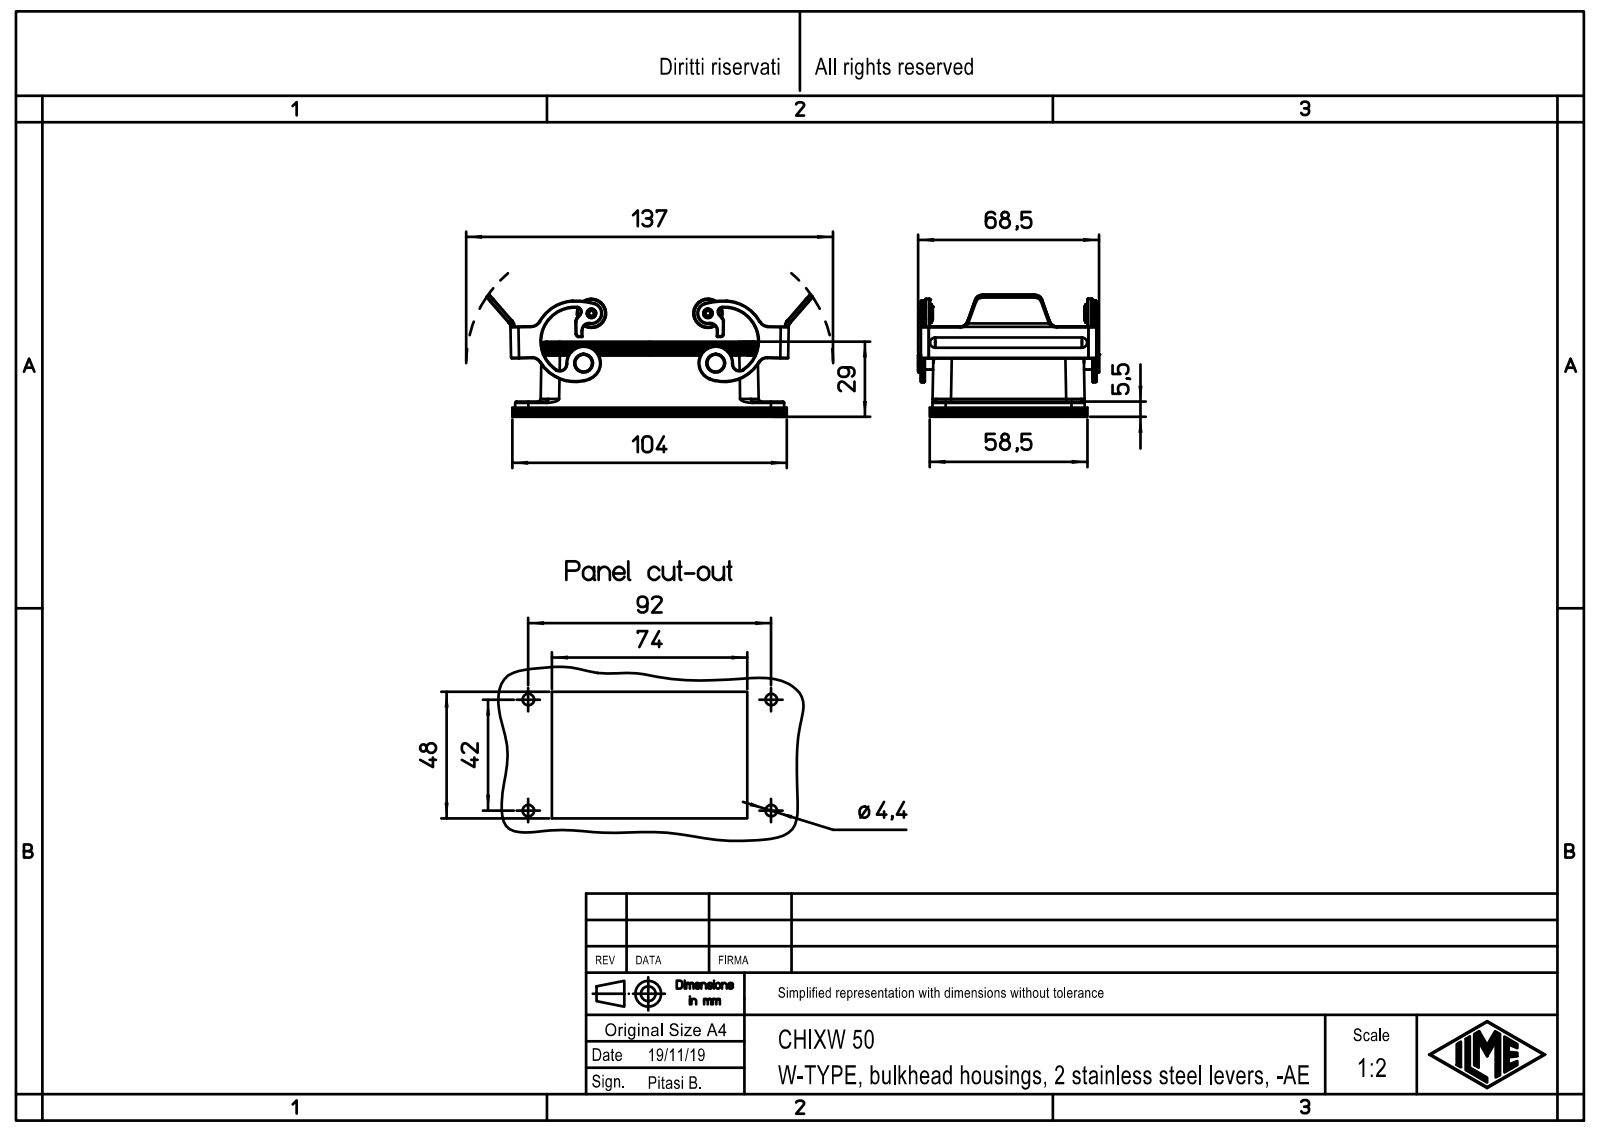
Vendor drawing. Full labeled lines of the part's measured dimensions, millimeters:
Part name (STEP PRODUCT): Leva; Leva.1; CHIXW 50
STEP written by: Creo Elements/Direct Modeling 20.1B 02-Apr-2019 (C) Parametric Technology GmbH (AUTOMOTIVE_DESIGN)
Units: millimetres
Bodies: 3 solids, 437 faces (163 planar, 218 cylindrical, 56 other)
Overall size (bounding box): 122.79 × 68.5 × 46.95
Volume: 45 432 mm³ · Surface area: 33 187 mm²
Round holes (diameter × count): ⌀3 ×4, ⌀4.9 ×4, ⌀5 ×4, ⌀1.2 ×2, ⌀2 ×2, ⌀3.1 ×2
Round bosses / shafts (diameter × count): ⌀7 ×4, ⌀4.8 ×4, ⌀3 ×4, ⌀11 ×2, ⌀3.5 ×2
Partial cylindrical surfaces — rounded edges, fillets, slot ends (radius × count): R3 ×12, R4 ×12, R2 ×8, R1.5 ×6, R3.5 ×6, R2.5 ×4, R5 ×4, R7 ×4
Main face-to-face distances: 1.5, 4.11, 65, 5.8, 103.4, 66.5, 63.5, 1, 52.83, 3.5
Hole centre spacings: 12.09, 46.09, 80.01, 91.54, 19.08, 43, 46, 50.39
